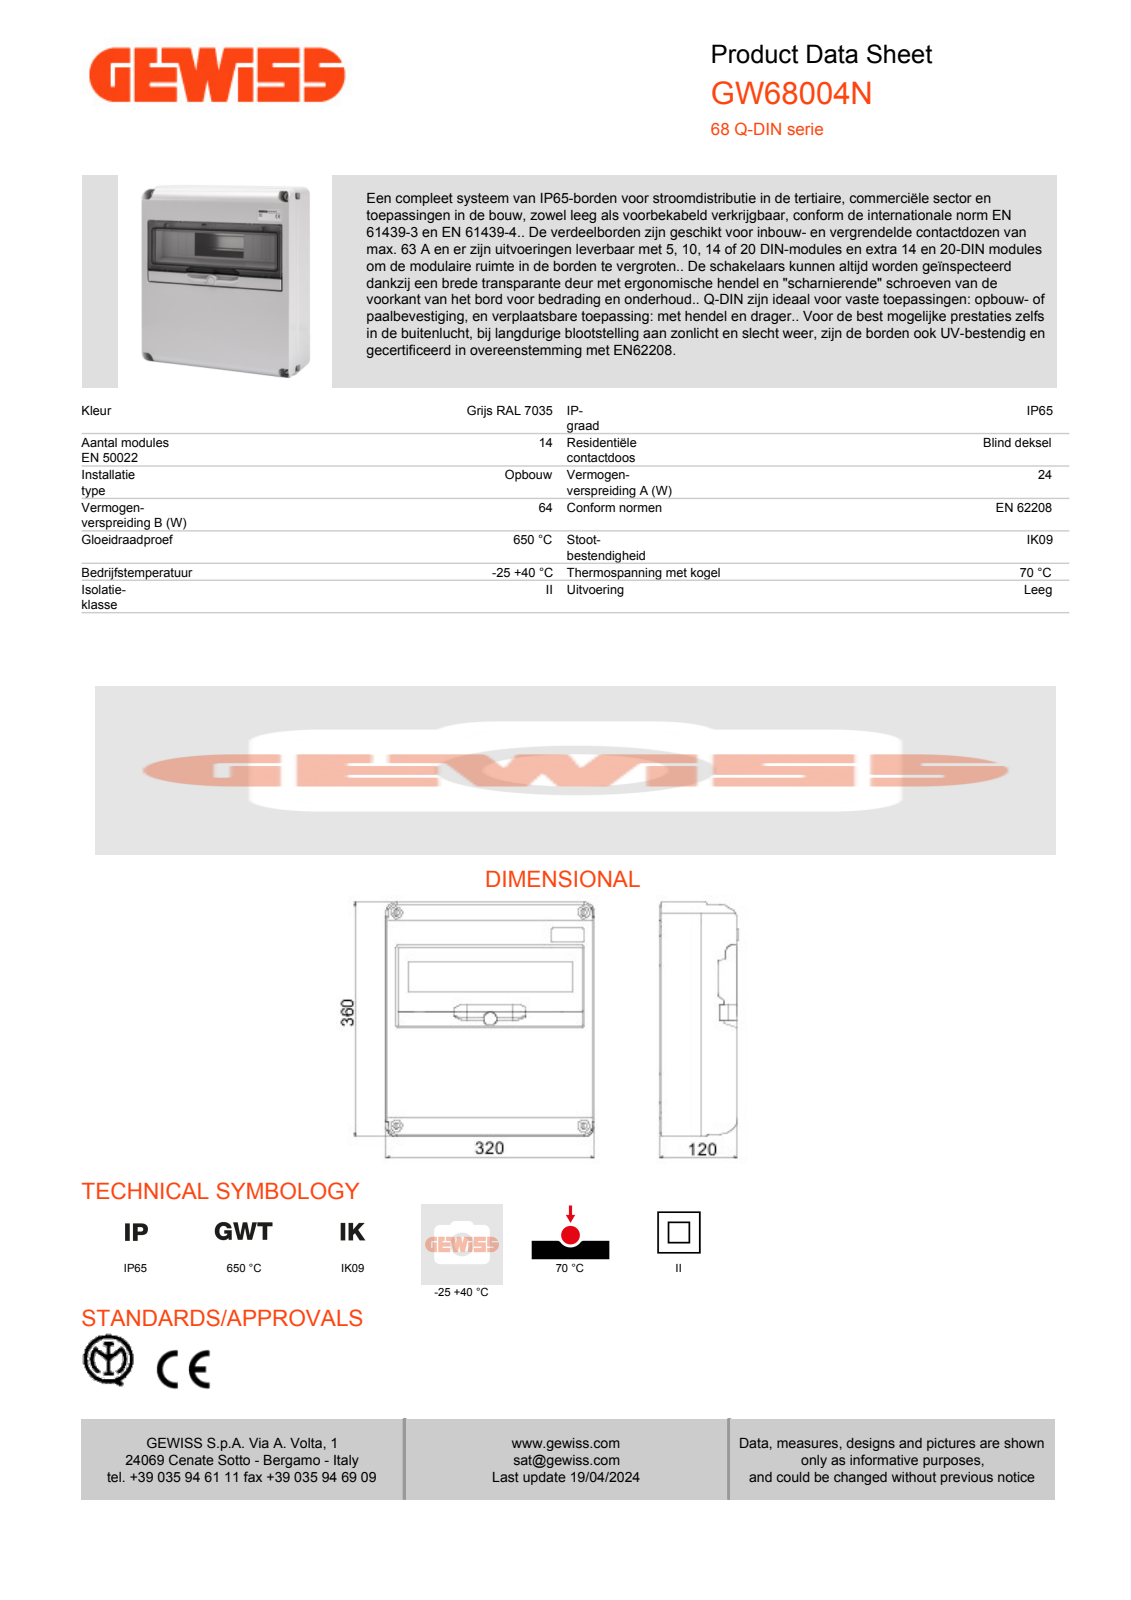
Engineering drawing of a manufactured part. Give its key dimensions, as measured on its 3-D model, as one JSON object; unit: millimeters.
{"part_name": "55530422AXXX_TAB_FONDO_QDIN_14M; 55523922F__FRONTALE_14M_1GR_LIS; GW68004N_ASM", "step_written_by": "CREO PARAMETRIC BY PTC INC, 2020354 (CONFIG_CONTROL_DESIGN)", "units": "millimeters", "bodies": {"solids": 2, "faces": 828, "planar": 516, "cylindrical": 118, "other": 194}, "overall_size": [360.75, 320.85, 122.49], "volume_mm3": 2576000, "surface_area_mm2": 840016, "partial_cylinders_radius": [[1.5, 25], [2, 20], [1, 8], [3.5, 8], [0.5, 6], [4.5, 4], [13, 4], [16, 4]], "face_to_face_distances": [3, 115.3, 118.3, 112.3, 313.72, 320.01, 35, 360, 83.3, 80.3]}
